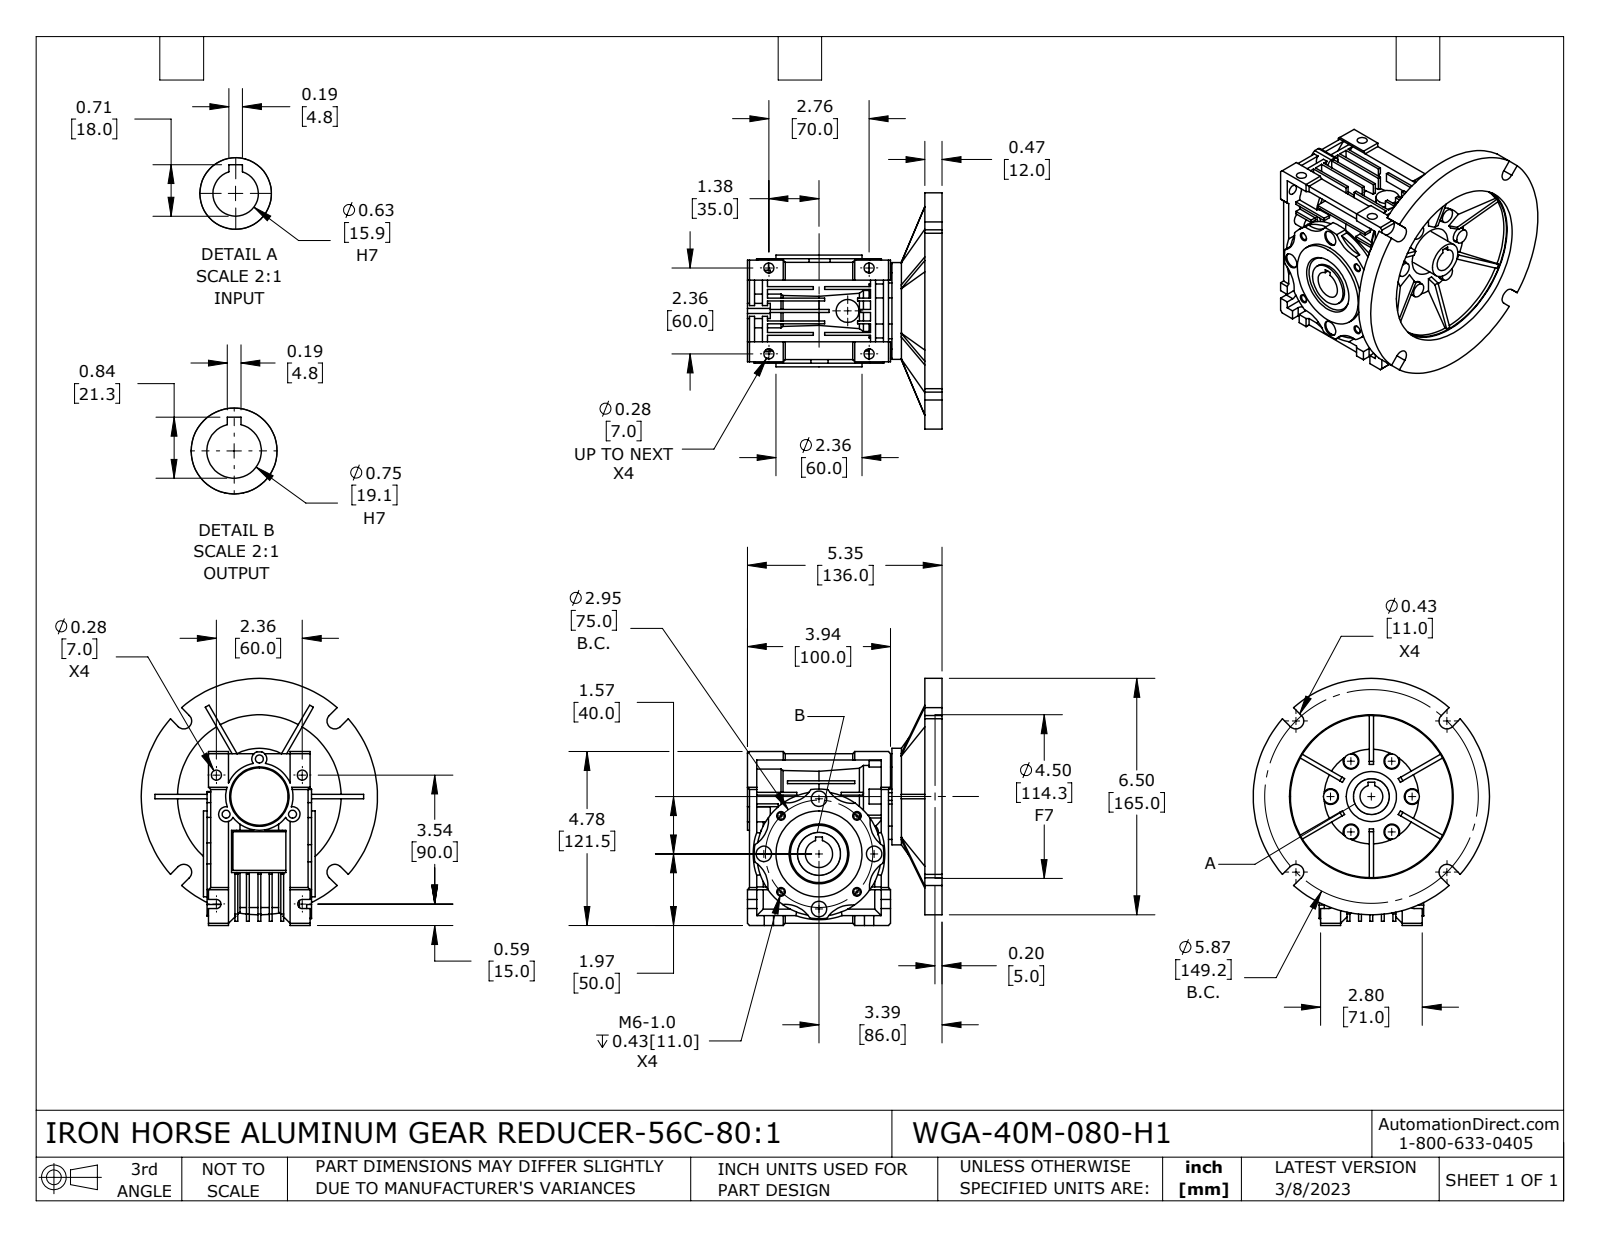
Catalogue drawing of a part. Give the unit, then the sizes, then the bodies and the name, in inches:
Units: inches
Overall size (bounding box): 6.791 × 6.496 × 5.354
Round holes (diameter × count): ⌀0.276 ×6, ⌀0.433 ×6, ⌀0.194 ×4, ⌀0.425 ×4, ⌀0.219 ×3, ⌀0.625 ×1, ⌀0.65 ×1, ⌀0.75 ×1, ⌀0.906 ×1, ⌀1.102 ×1, ⌀1.181 ×1, ⌀1.378 ×1
Round bosses / shafts (diameter × count): ⌀0.394 ×6, ⌀6.496 ×1, ⌀2.953 ×1, ⌀2.657 ×1, ⌀2.362 ×1, ⌀2.126 ×1, ⌀1.85 ×1, ⌀1.417 ×1
Partial cylindrical surfaces — rounded edges, fillets, slot ends (radius × count): R0.787 ×8, R0.126 ×6, R0.206 ×6, R0.217 ×4, R0.207 ×3, R1.713 ×1, R1.716 ×1, R1.781 ×1
Main face-to-face distances: 0.315, 0.472, 0.079, 0.945, 0.236, 0.059, 0.63, 0.098, 0.394, 0.197
Hole centre spacings: 1.122, 1.146, 2.765, 1.943, 1.476, 1.516, 2.088, 2.144
Volume: 50.34 in³ · Surface area: 315 in²
Bodies: 4 solids, 856 faces (511 planar, 251 cylindrical, 94 other)
Part name (STEP PRODUCT): WGA-40M-080-H1
STEP written by: SolidWorks 2021 (CONFIG_CONTROL_DESIGN)
